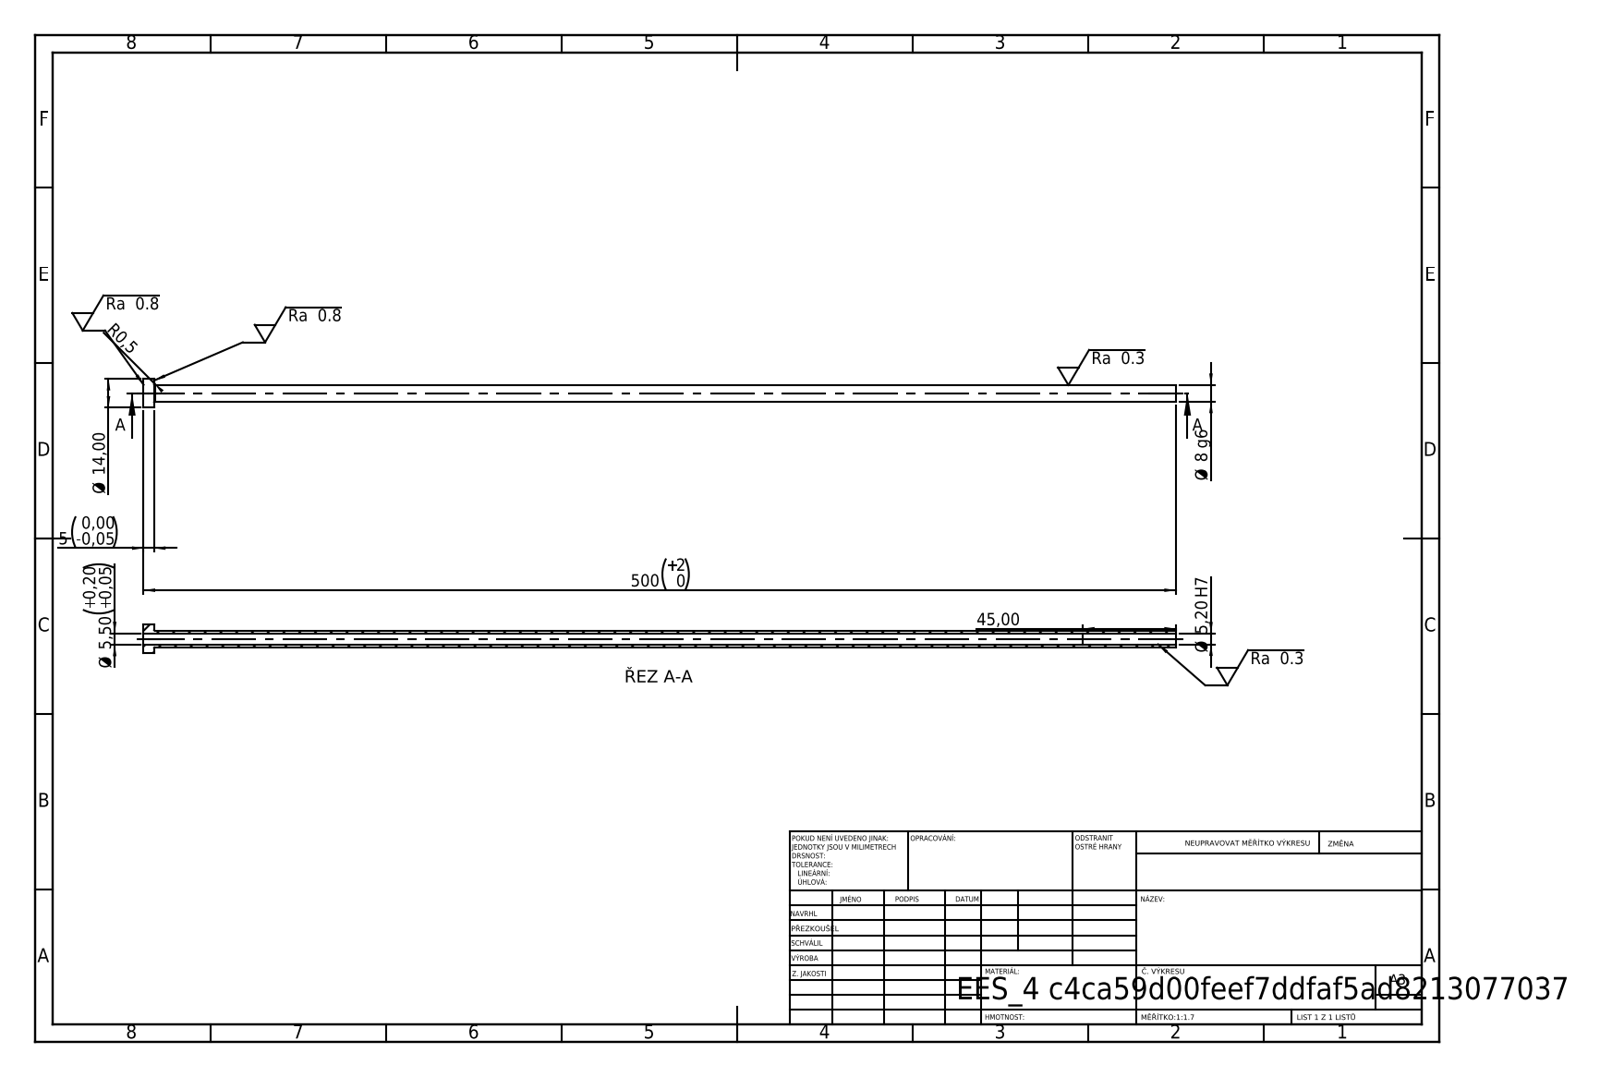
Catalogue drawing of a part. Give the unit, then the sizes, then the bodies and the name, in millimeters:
Units: millimetres
Overall size (bounding box): 500 × 14 × 14
Round holes (diameter × count): ⌀5.2 ×1, ⌀5.5 ×1
Round bosses / shafts (diameter × count): ⌀14 ×1, ⌀8 ×1
Main face-to-face distances: 5, 500, 495, 455, 450, 45
Volume: 13 887 mm³ · Surface area: 21 518 mm²
Bodies: 1 solid, 14 faces (4 planar, 8 cylindrical, 2 other)
STEP written by: SolidWorks 2019 (CONFIG_CONTROL_DESIGN)
